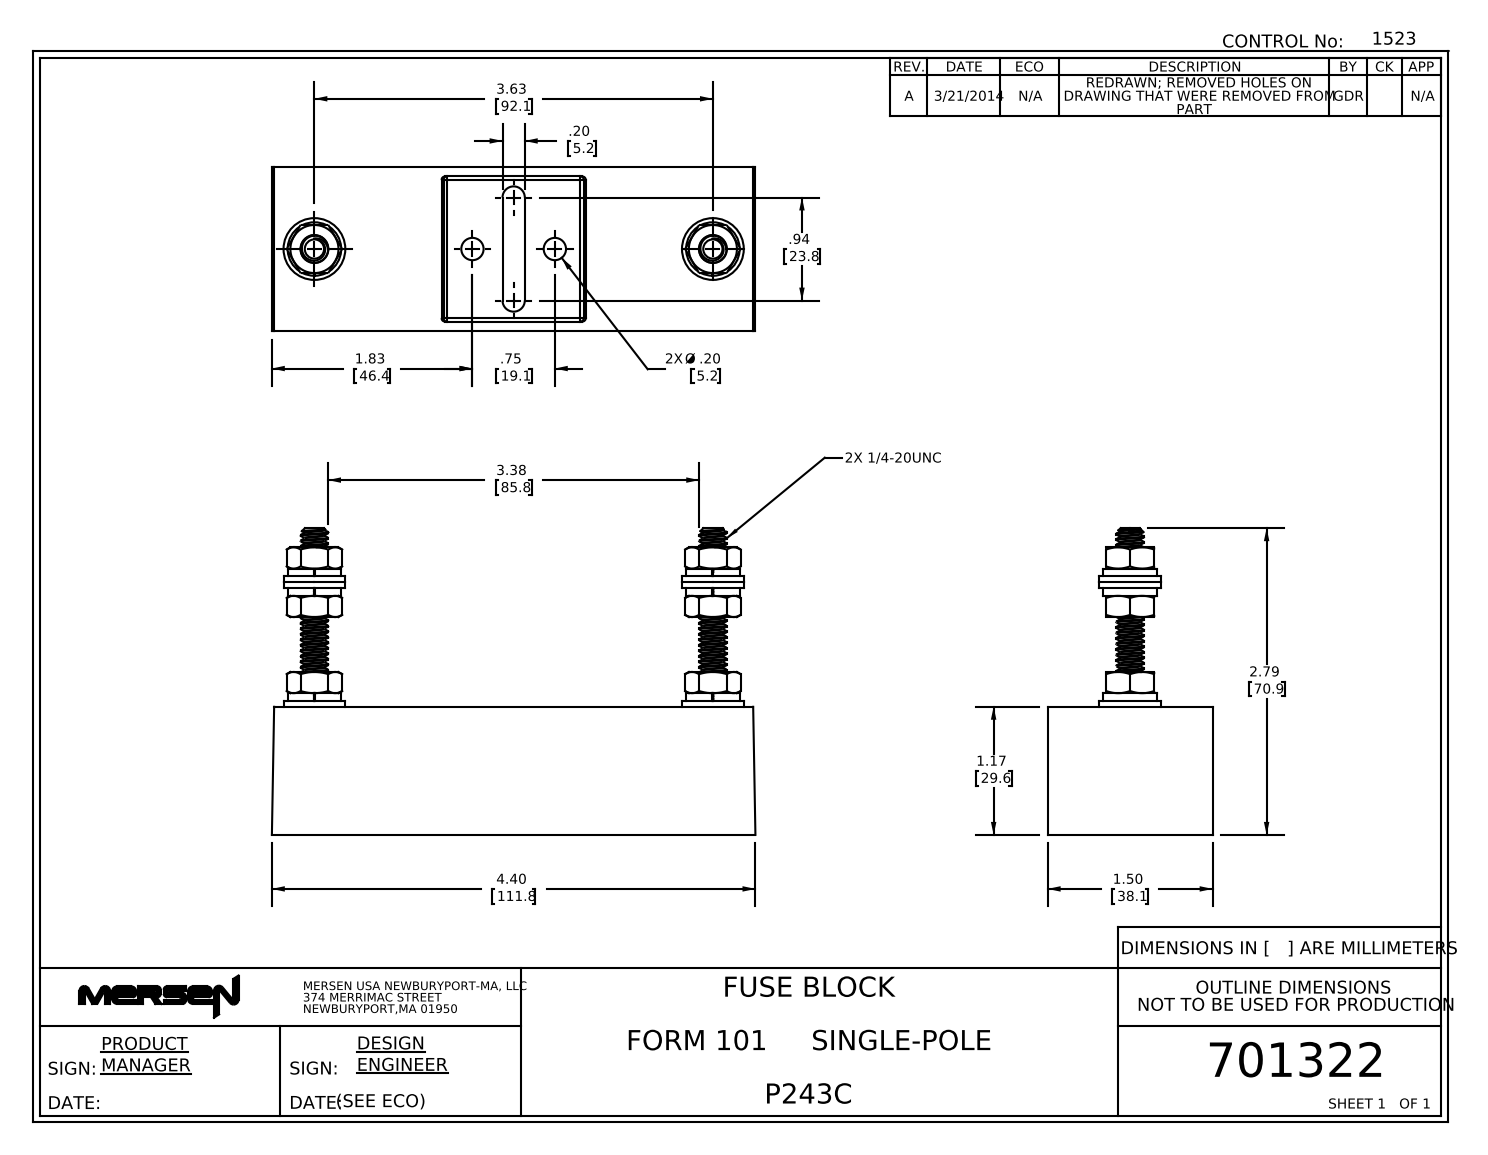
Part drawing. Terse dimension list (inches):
name: 701322rev
written by: SolidWorks 2013 (AUTOMOTIVE_DESIGN)
unit: in
bodies: 21 solids, 834 faces (227 planar, 345 cylindrical, 262 other)
size: 4.4 × 2.79 × 1.5
volume: 2.649 in³; area: 59.13 in²
holes: 2× ⌀0.185, 2× ⌀0.203, 2× ⌀0.252, 2× ⌀0.265
bosses: 2× ⌀0.682, 2× ⌀0.562, 2× ⌀0.487, 2× ⌀0.25
rounds: 22× R0.03, 12× R0.02, 2× R0.101
face distances: 1.5, 0.09, 0.125, 1.04, 1.165, 2.836, 0.092, 2.928, 1.41, 2.837
hole spacings: 1.438, 2.188, 0.75, 3.626
